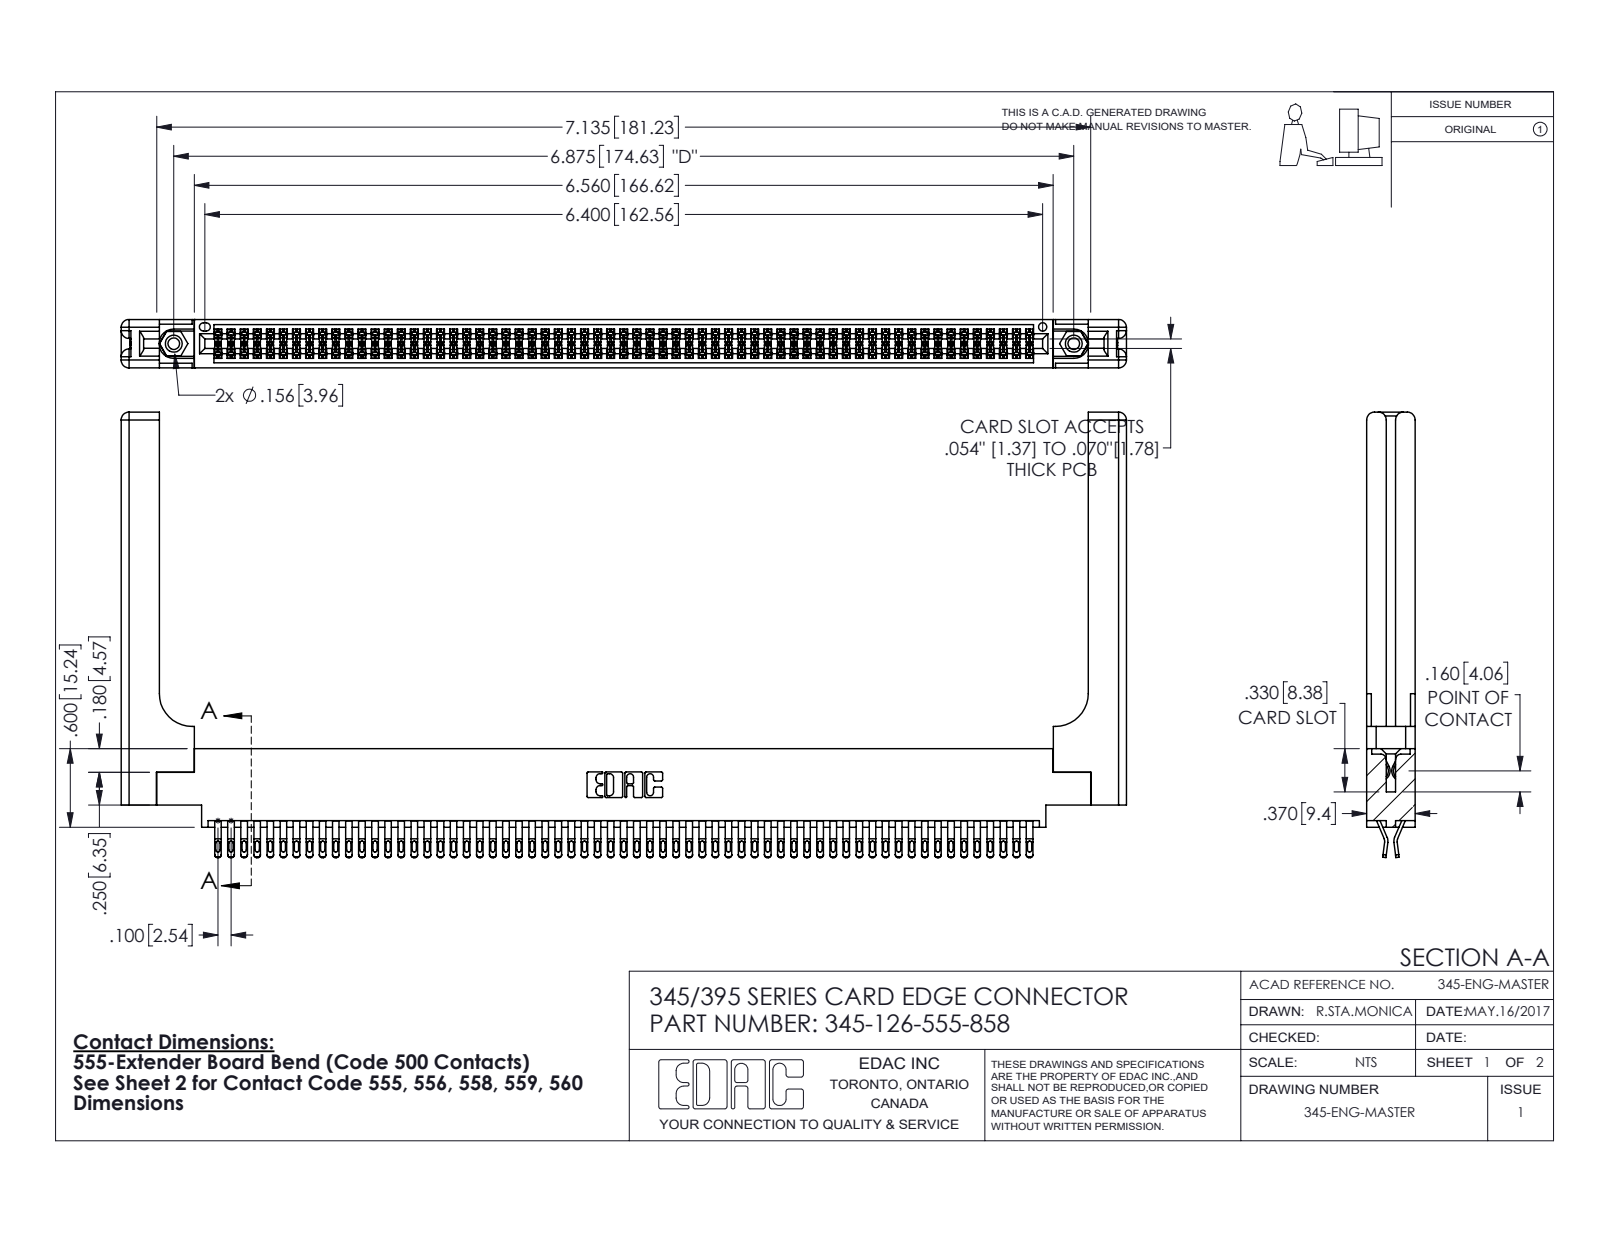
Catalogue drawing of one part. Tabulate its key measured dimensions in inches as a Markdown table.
| quantity | value |
| --- | --- |
| part name | 345-292-001_555 Tail; 345-220-058_345-220-058; 345-250-001_345-250-001-102; 345 Part_0.170 Offset - 0.156 Dia-TH (+1 more) |
| STEP written by | SolidWorks 2016 (CONFIG_CONTROL_DESIGN) |
| units | inches |
| bodies | 131 solids, 7442 faces (4138 planar, 3244 cylindrical, 60 other) |
| overall size | 7.679 × 3.402 × 0.37 |
| volume | 1.701 in³ |
| surface area | 55.1 in² |
| round holes (diameter × count) | 0.089 × 2, 0.125 × 2, 0.156 × 2, 0.064 × 1 |
| round bosses / shafts (diameter × count) | 0.155 × 2 |
| partial cylindrical surfaces (radius × count) | 0.016 × 315, 0.02 × 252, 0.006 × 189, 0.01 × 22, 0.06 × 16, 0.007 × 6, 0.031 × 6, 0.026 × 3 |
| main face-to-face distances | 0.072, 0.298, 0.37, 0.025, 0.098, 0.272, 0.2, 0.225, 0.175, 0.148 |
| hole center spacings | 0.27, 6.639, 6.875 |
